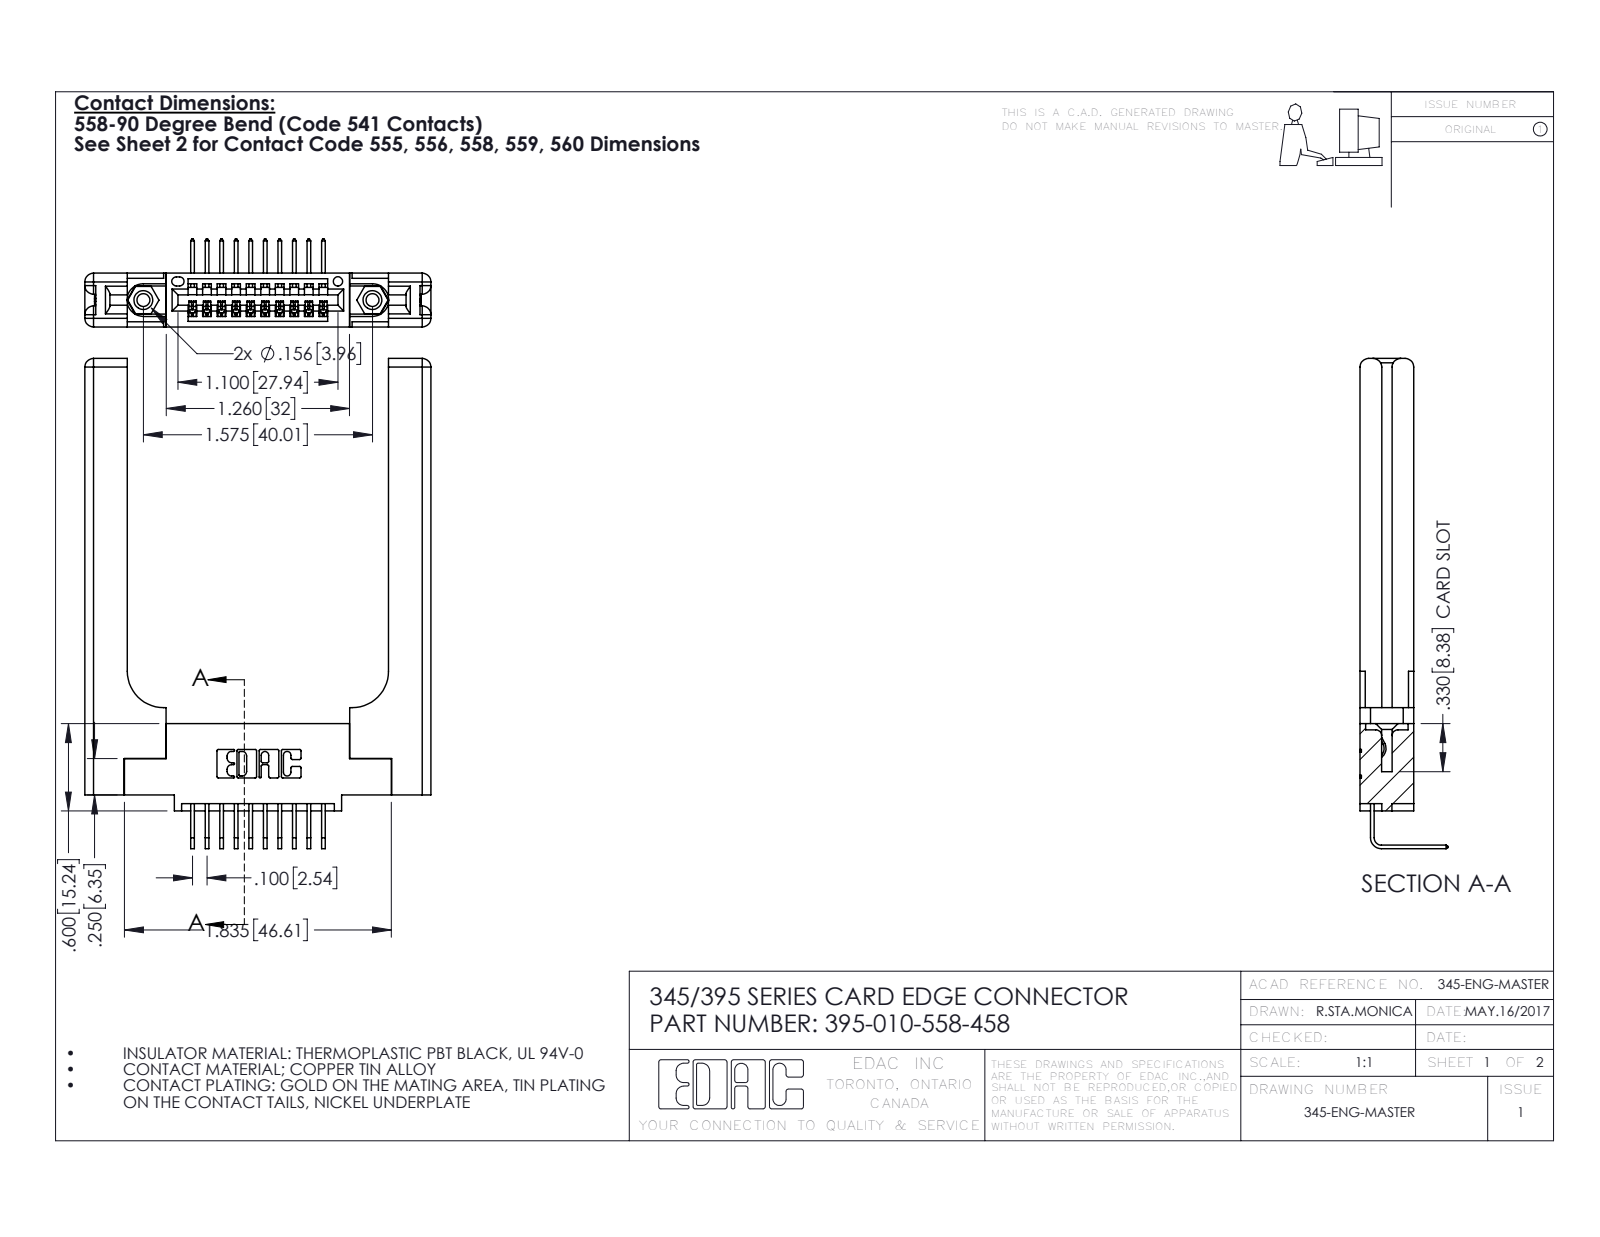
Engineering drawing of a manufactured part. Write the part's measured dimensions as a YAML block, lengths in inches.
part_name: "345-250-001_345-250-001-102; 395-010-558-458; 345-220-058_345-220-058; 345 Part_0.110 Offset - 0.156 Dia-TH (+1 more)"
step_written_by: "SolidWorks 2016 (CONFIG_CONTROL_DESIGN)"
units: inches
bodies: {solids: 15, faces: 986, planar: 652, cylindrical: 274, other: 60}
overall_size: [3.369, 2.379, 0.605]
volume: 0.851
surface_area: 19.18
round_holes:
  - {diameter: 0.089, count: 2}
  - {diameter: 0.125, count: 2}
  - {diameter: 0.156, count: 2}
  - {diameter: 0.064, count: 1}
round_bosses_or_shafts:
  - {diameter: 0.155, count: 2}
partial_cylinders:
  - {radius: 0.01, count: 22}
  - {radius: 0.006, count: 20}
  - {radius: 0.06, count: 16}
  - {radius: 0.007, count: 6}
  - {radius: 0.031, count: 6}
  - {radius: 0.026, count: 3}
  - {radius: 0.03, count: 2}
  - {radius: 0.031, count: 2}
face_to_face_distances: [0.37, 0.15, 0.072, 0.22, 0.077, 0.148, 0.298, 1.796, 0.071, 0.2]
hole_center_spacings: [0.27, 1.344, 1.575]
